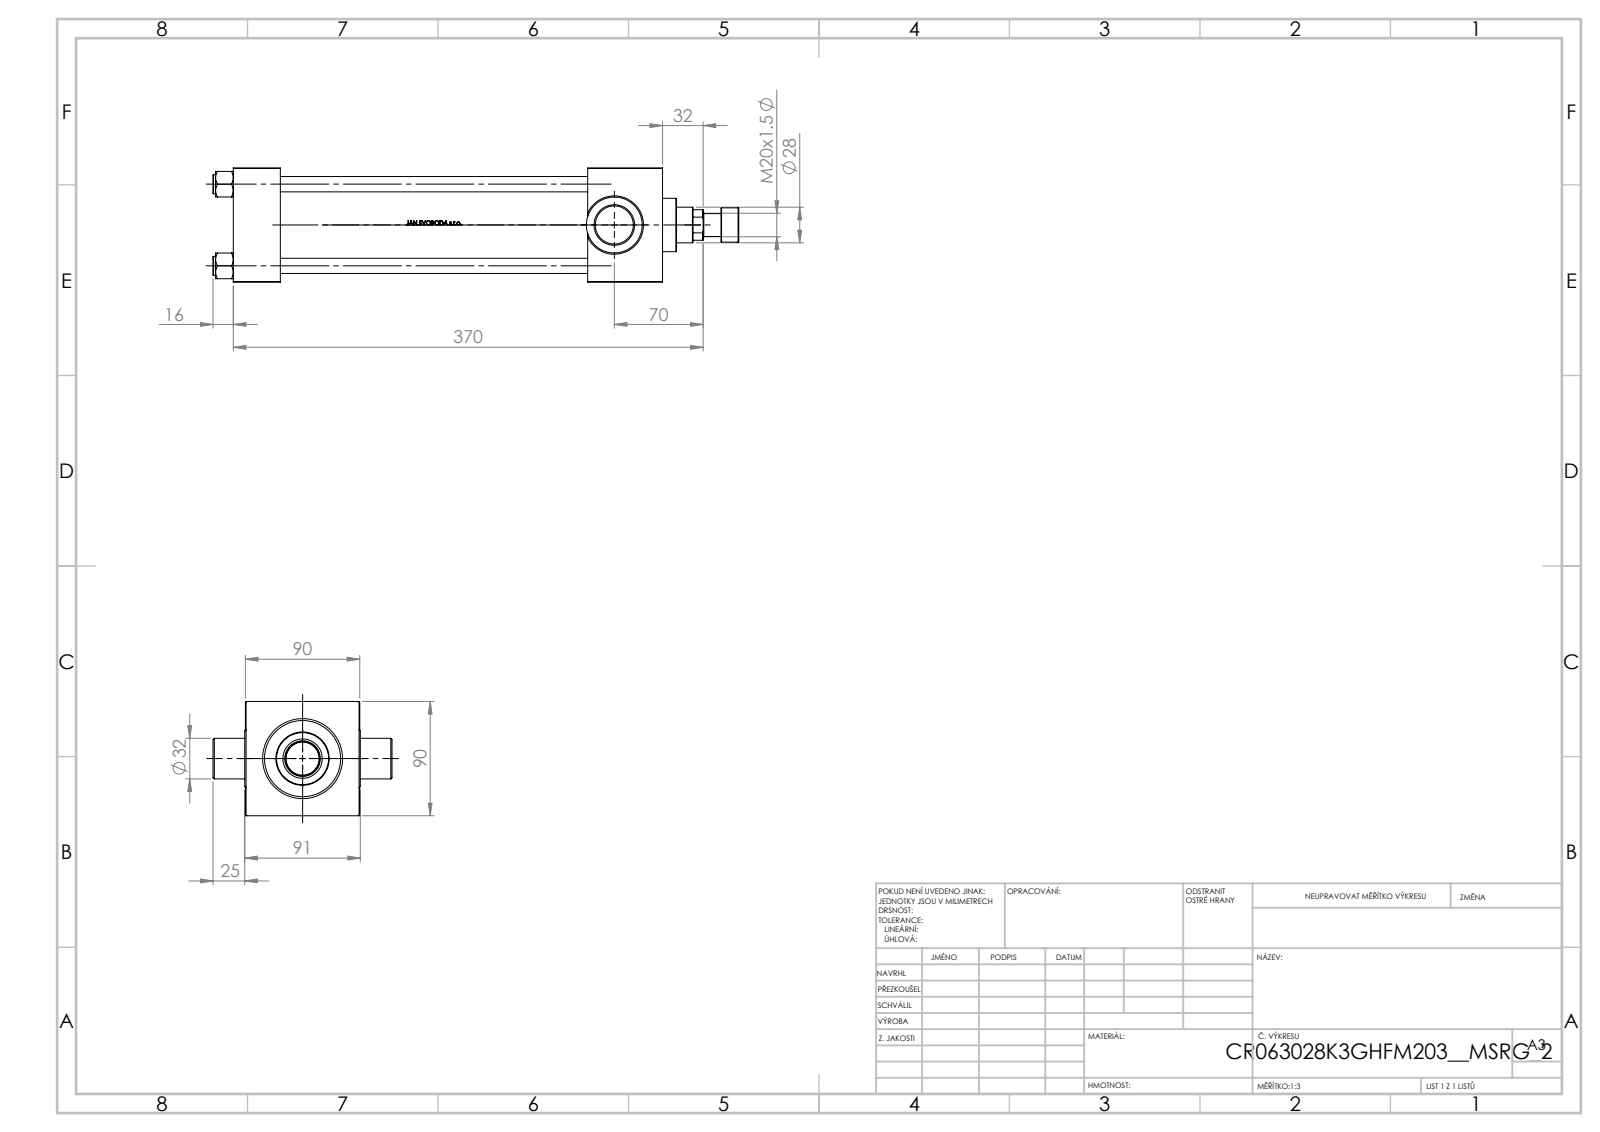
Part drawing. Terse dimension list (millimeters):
name: V215CR_K_Body; NUT_M5_K; V215_VC_A; V215CR_K_TYCINKA (+2 more)
written by: SolidWorks 2019 (CONFIG_CONTROL_DESIGN)
unit: mm
bodies: 12 solids, 1079 faces (433 planar, 116 cylindrical, 530 other)
size: 414 × 141 × 90
volume: 1 325 000 mm³; area: 299 648 mm²
holes: 4× ⌀12, 1× ⌀7, 1× ⌀18.5, 1× ⌀28, 1× ⌀31, 1× ⌀50, 1× ⌀60, 1× ⌀63
bosses: 4× ⌀15, 1× ⌀69, 1× ⌀42, 1× ⌀32, 1× ⌀27, 1× ⌀18
rounds: 1× R22
face distances: 90, 37, 0.5, 89.5, 338, 301, 242, 279, 59, 89
hole spacings: 45.47, 64.3, 90.93
